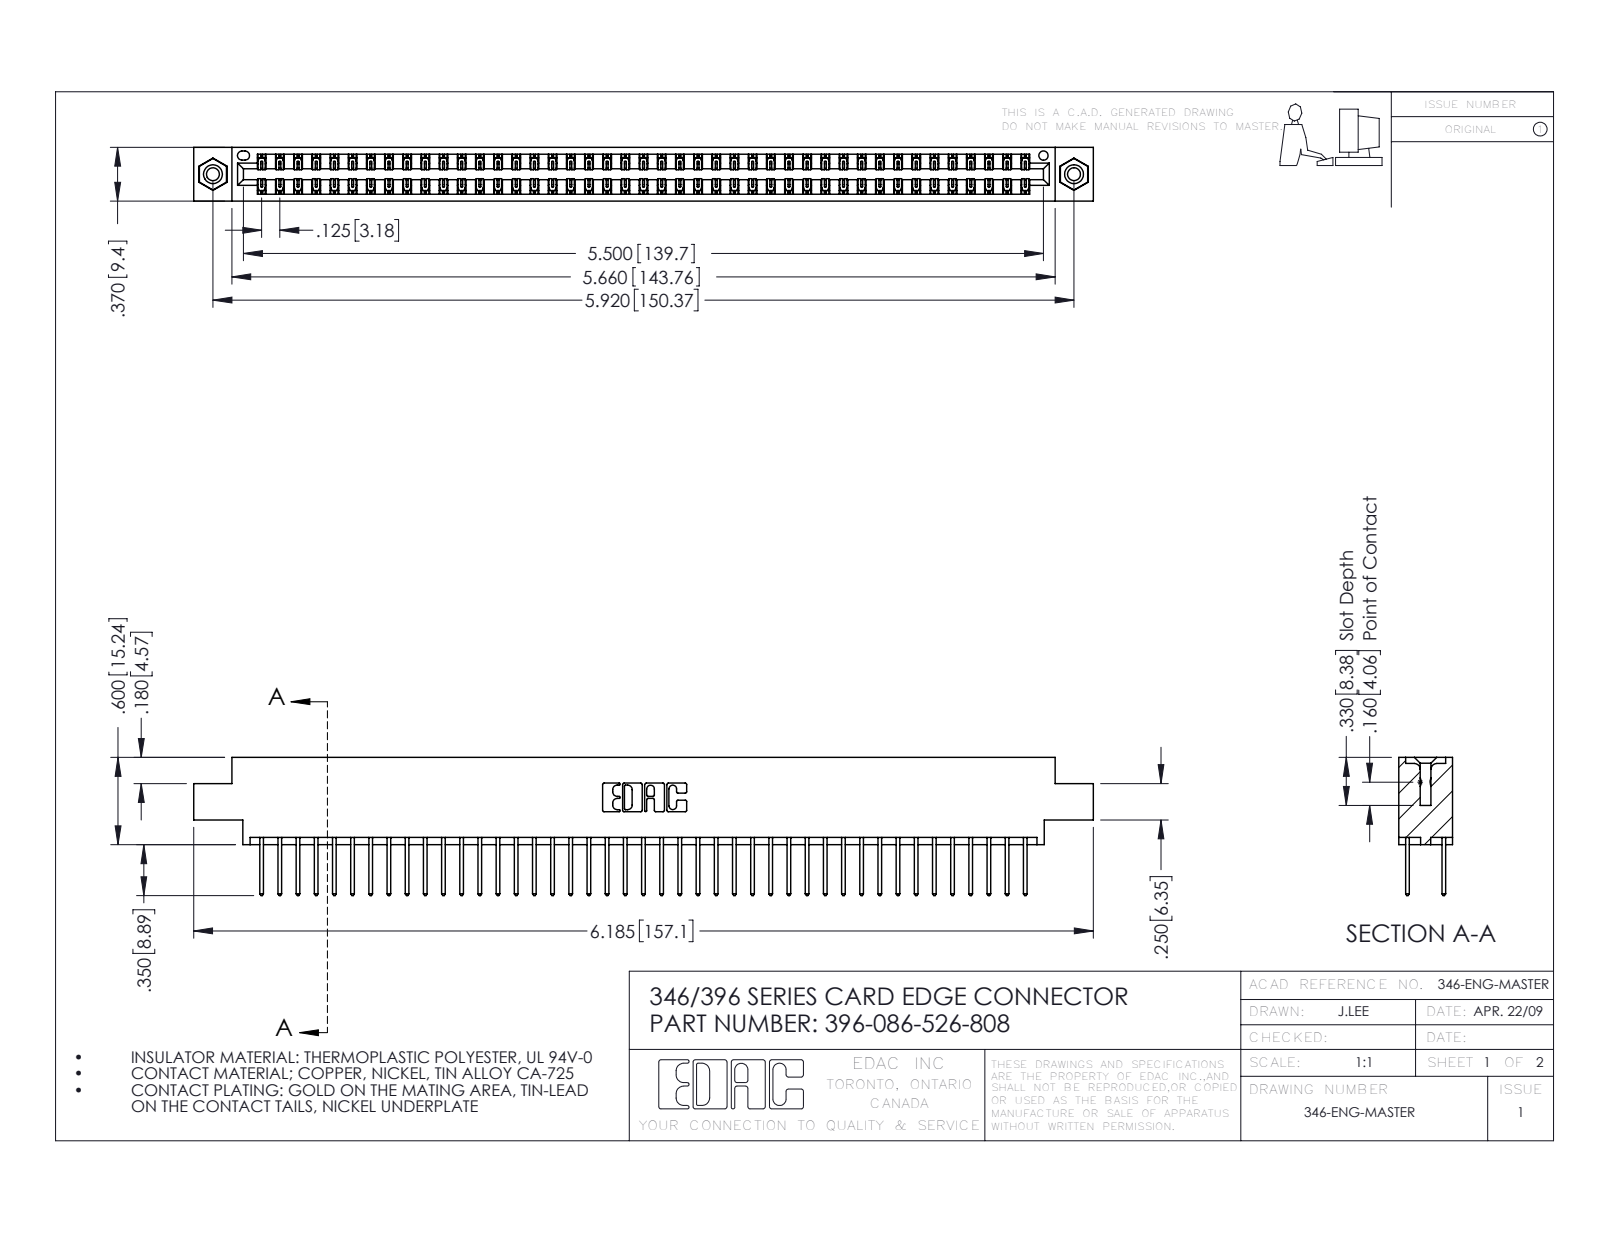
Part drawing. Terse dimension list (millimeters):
name: 345-292-001_345-293-126; 346 Part_0.170 Offset - 0.156 Dia-TI; 396-086-526-808; 345-250-001_345-250-003-102
written by: SolidWorks 2016 (CONFIG_CONTROL_DESIGN)
unit: mm
bodies: 89 solids, 4658 faces (3122 planar, 1520 cylindrical, 16 other)
size: 157.1 × 24.1 × 9.4
volume: 15 300 mm³; area: 21 880 mm²
holes: 2× ⌀2.3, 2× ⌀3.2, 2× ⌀4, 1× ⌀1.6
bosses: 2× ⌀3.9
rounds: 129× R0.2, 86× R0.3, 22× R0.3, 6× R0.2, 6× R0.8, 3× R0.7, 2× R0.4, 2× R0.6
face distances: 1.2, 8.2, 6.4, 9.4, 1.8, 7.6, 0.6, 7, 5.6, 3.8
hole spacings: 6.2, 145.1, 150.4
